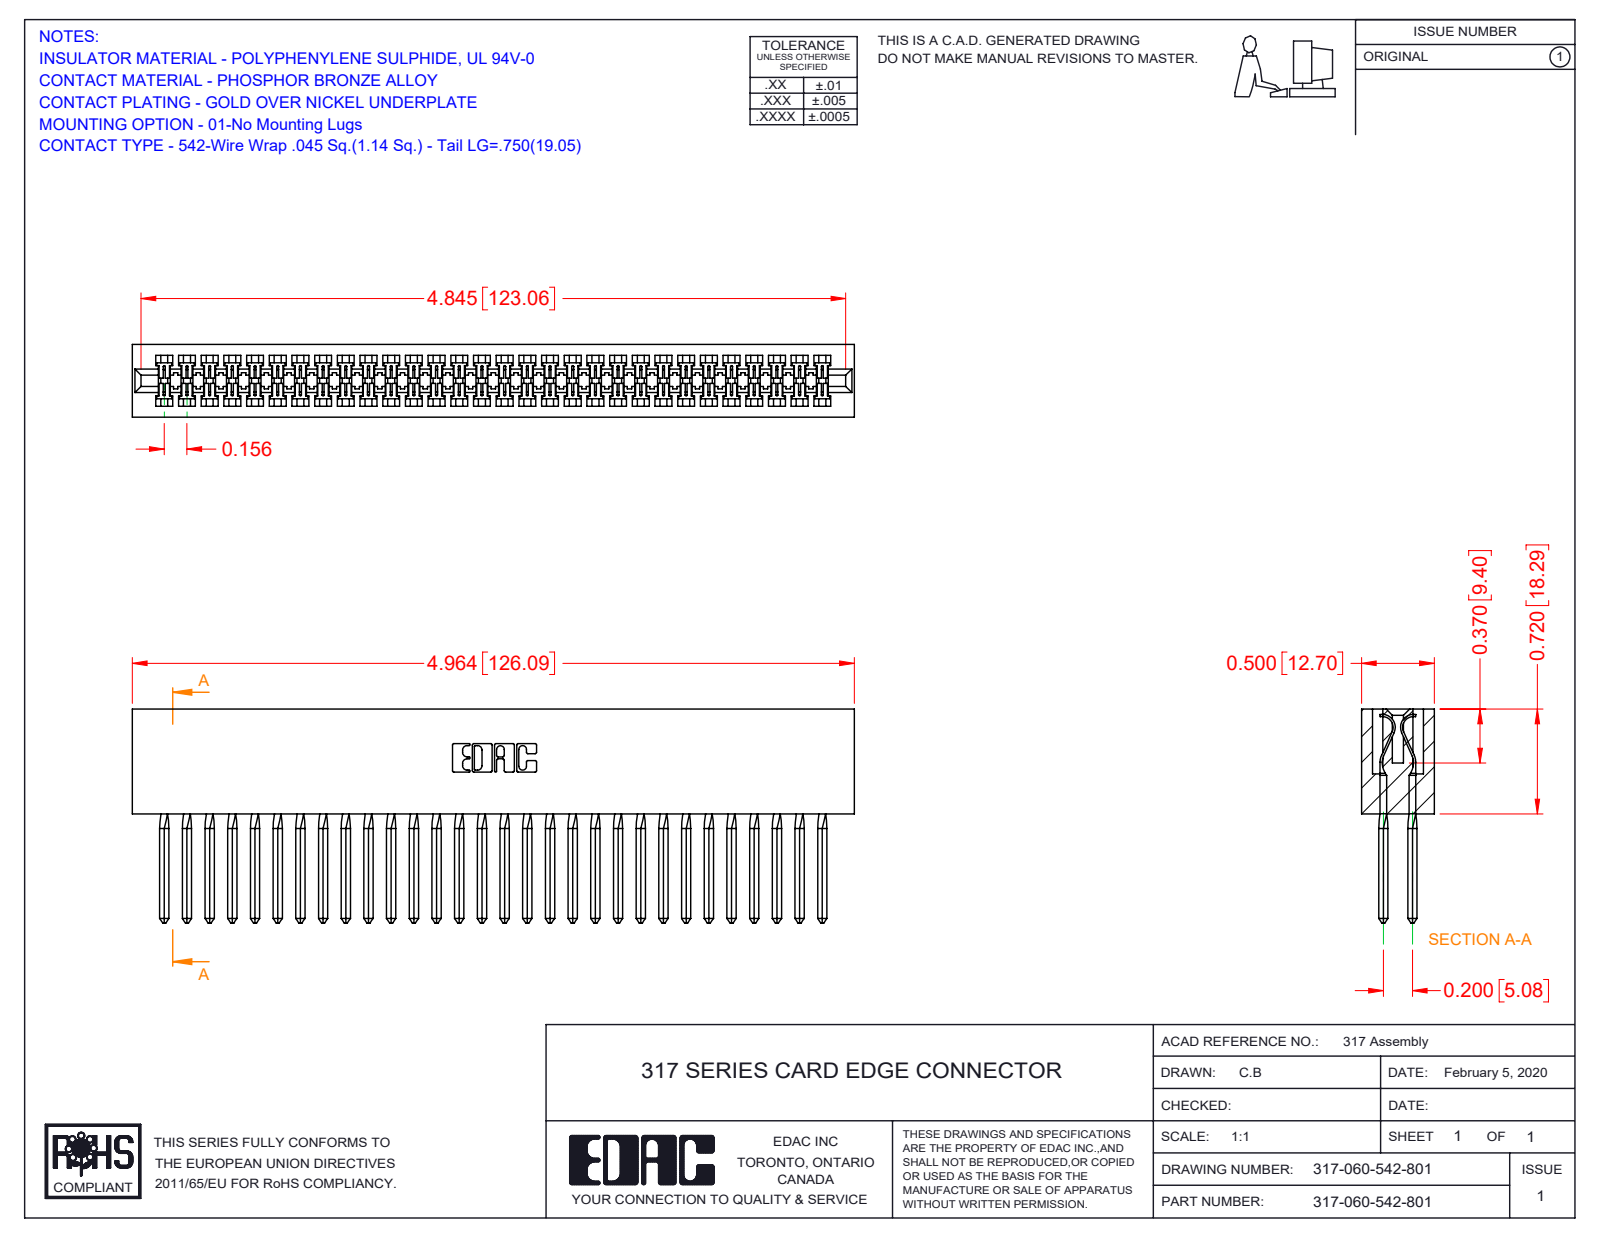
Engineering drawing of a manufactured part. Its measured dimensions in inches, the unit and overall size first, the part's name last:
Units: inches
Overall size (bounding box): 4.964 × 1.47 × 0.5
Partial cylindrical surfaces — rounded edges, fillets, slot ends (radius × count): R0.006 ×120, R0.01 ×22, R0.007 ×6, R0.031 ×6, R0.026 ×3, R0.074 ×2, R0.089 ×2, R0.1 ×2
Main face-to-face distances: 0.5, 0.075, 0.425, 0.35, 0.2, 0.116, 0.11, 0.046, 0.128, 0.372
Volume: 1.342 in³ · Surface area: 47.09 in²
Bodies: 61 solids, 3510 faces (2810 planar, 460 cylindrical, 240 other)
Part name (STEP PRODUCT): 317-060-542-801; 317-290-003_542; 317 Part_Lugless
STEP written by: SolidWorks 2016 (CONFIG_CONTROL_DESIGN)
